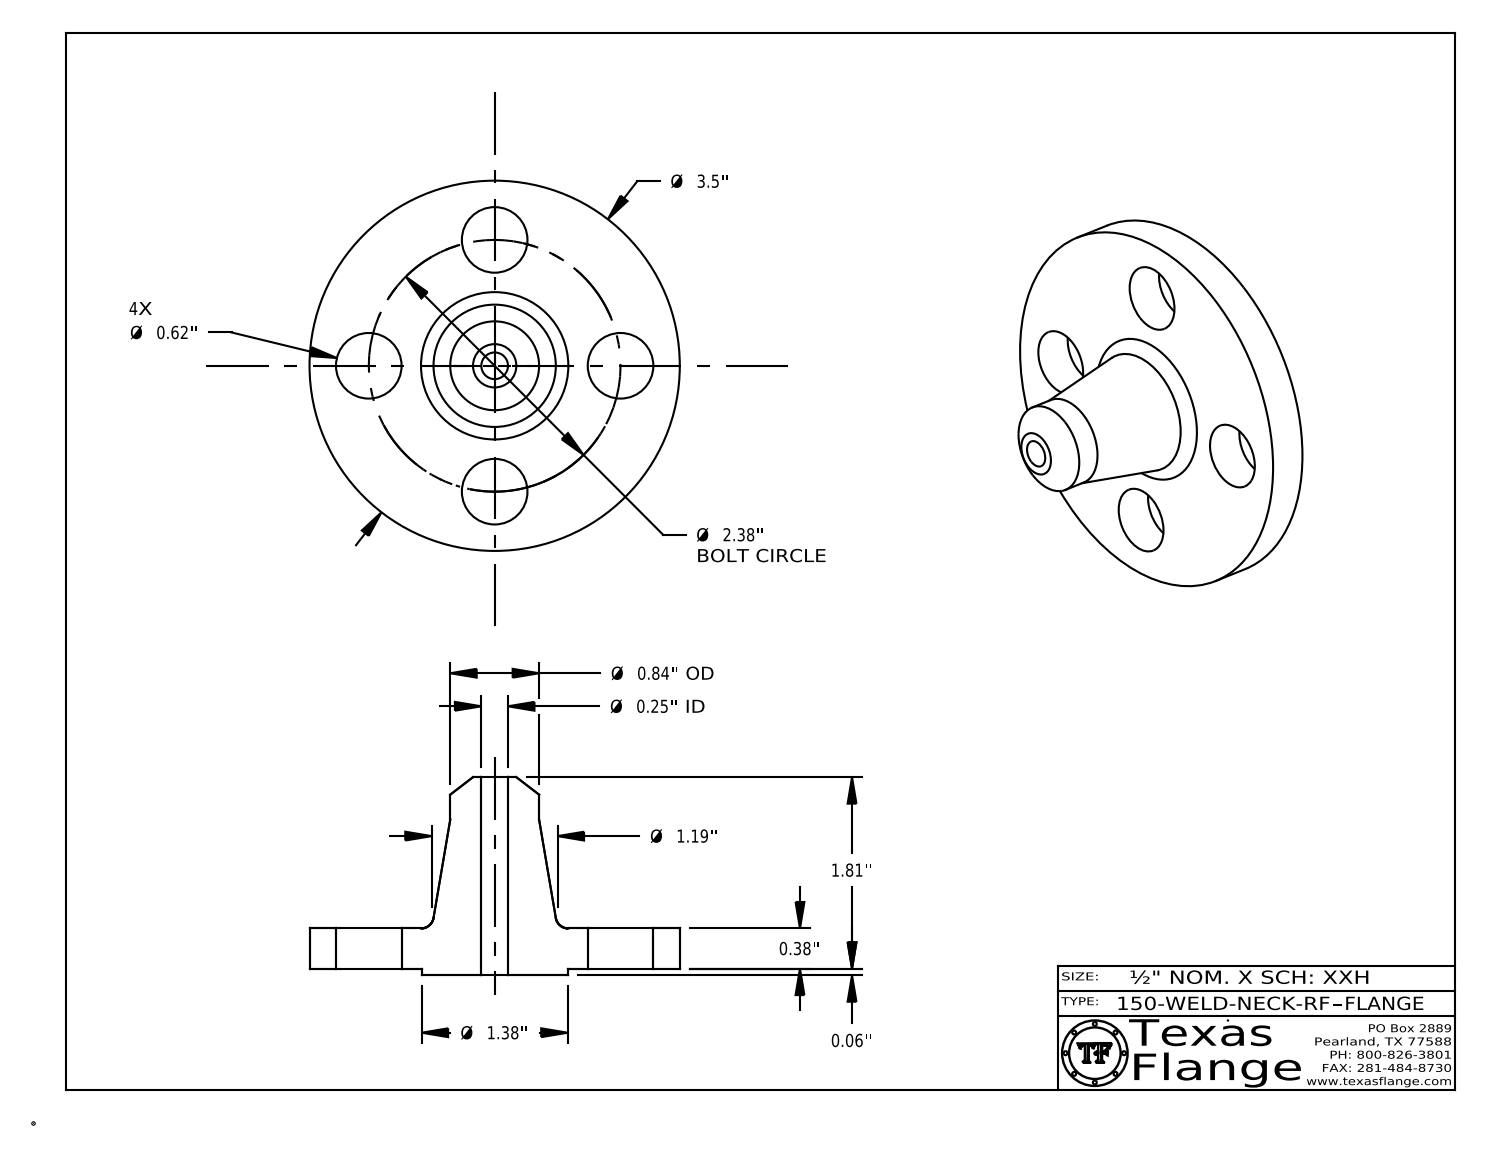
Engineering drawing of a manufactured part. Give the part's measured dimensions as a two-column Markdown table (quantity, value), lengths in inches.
| quantity | value |
| --- | --- |
| part name | 150-WELD-NECK-RF |
| STEP written by | CATIA V5 STEP AP214 (AUTOMOTIVE_DESIGN) |
| units | inches |
| bodies | 1 solid, 411 faces (369 planar, 36 cylindrical, 6 other) |
| overall size | 3.5 × 3.5 × 1.873 |
| volume | 4.228 in³ |
| surface area | 29.09 in² |
| round holes (diameter × count) | 0.62 × 4, 0.252 × 1, 0.495 × 1 |
| round bosses / shafts (diameter × count) | 0.03 × 8, 3.5 × 1, 1.38 × 1, 0.84 × 1, 0.39 × 1 |
| main face-to-face distances | 0.38, 0.063, 0.443, 1.872, 1.81, 1.43, 0.428, 0.365, 0.015, 1.445 |
| hole center spacings | 1.19, 1.683, 0.911, 2.199, 2.38, 1.19 |
